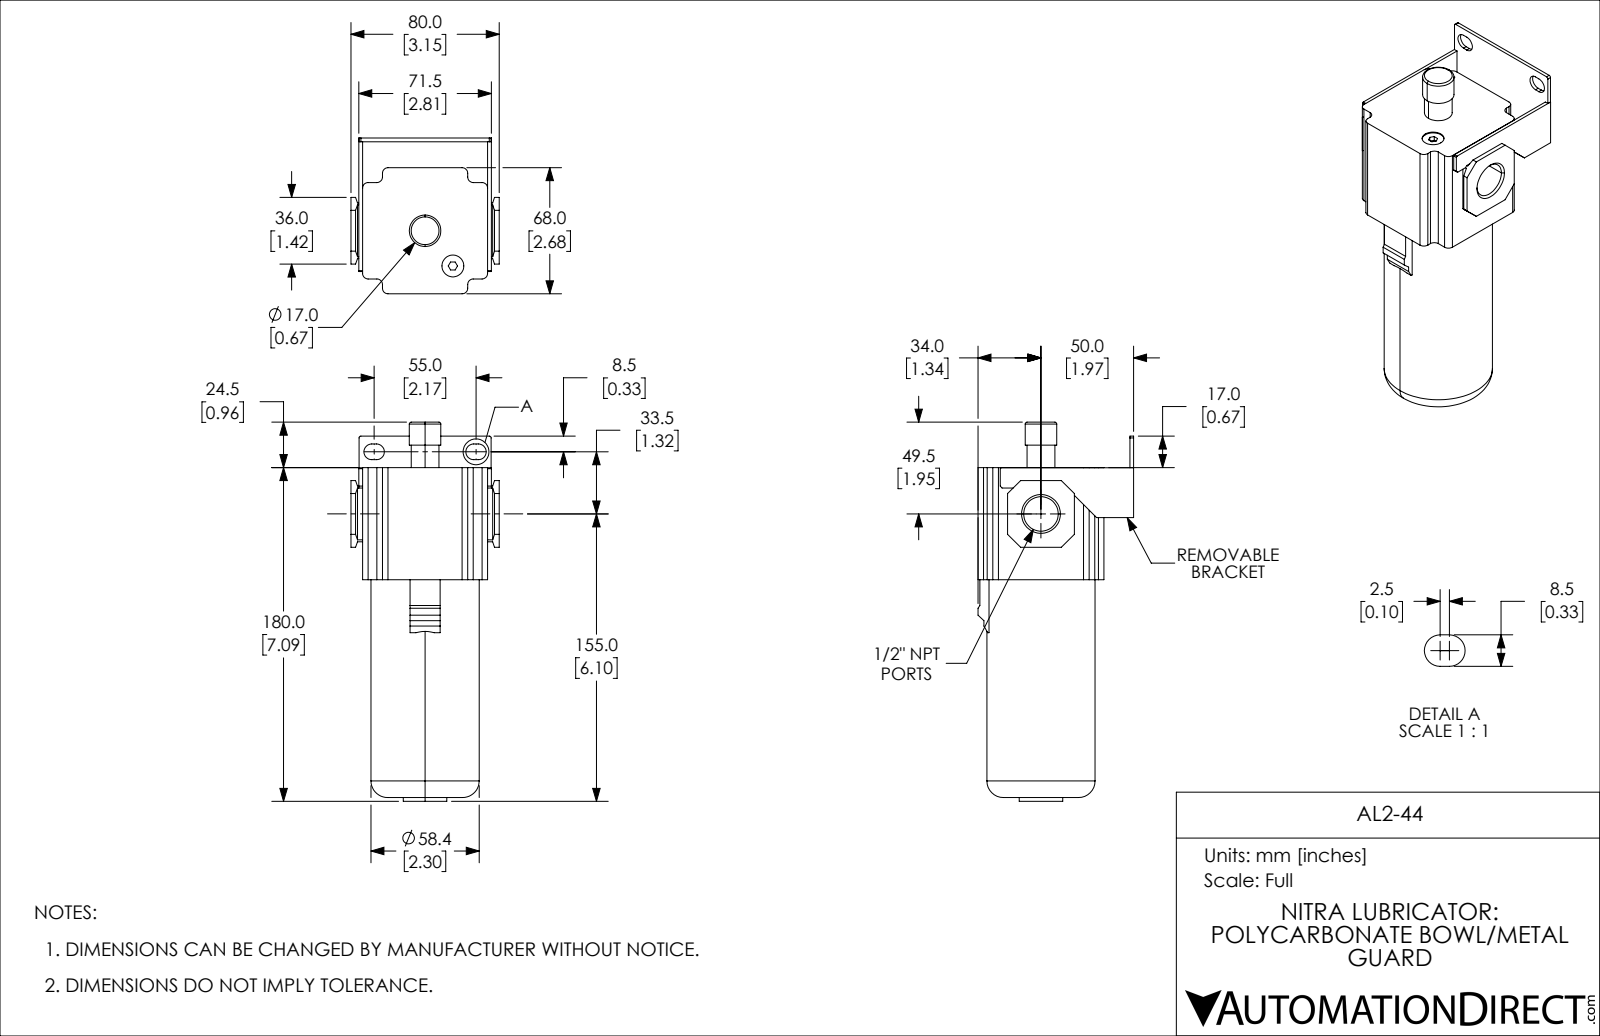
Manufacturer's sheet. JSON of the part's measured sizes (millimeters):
{"part_name": "AL2-44", "step_written_by": "SolidWorks 2019 (CONFIG_CONTROL_DESIGN)", "units": "millimeters", "bodies": {"solids": 1, "faces": 138, "planar": 98, "cylindrical": 32, "other": 8}, "overall_size": [204.5, 84, 80], "volume_mm3": 587687, "surface_area_mm2": 60840, "round_holes": [[11.8, 1], [18.63, 1]], "round_bosses_or_shafts": [[58.4, 1], [23.5, 1], [17, 1], [15, 1]], "partial_cylinders_radius": [[3, 12], [4.25, 4], [1, 2]], "face_to_face_distances": [2, 16, 68, 84, 82, 14, 69.5, 67.5, 4.25, 6.25]}
